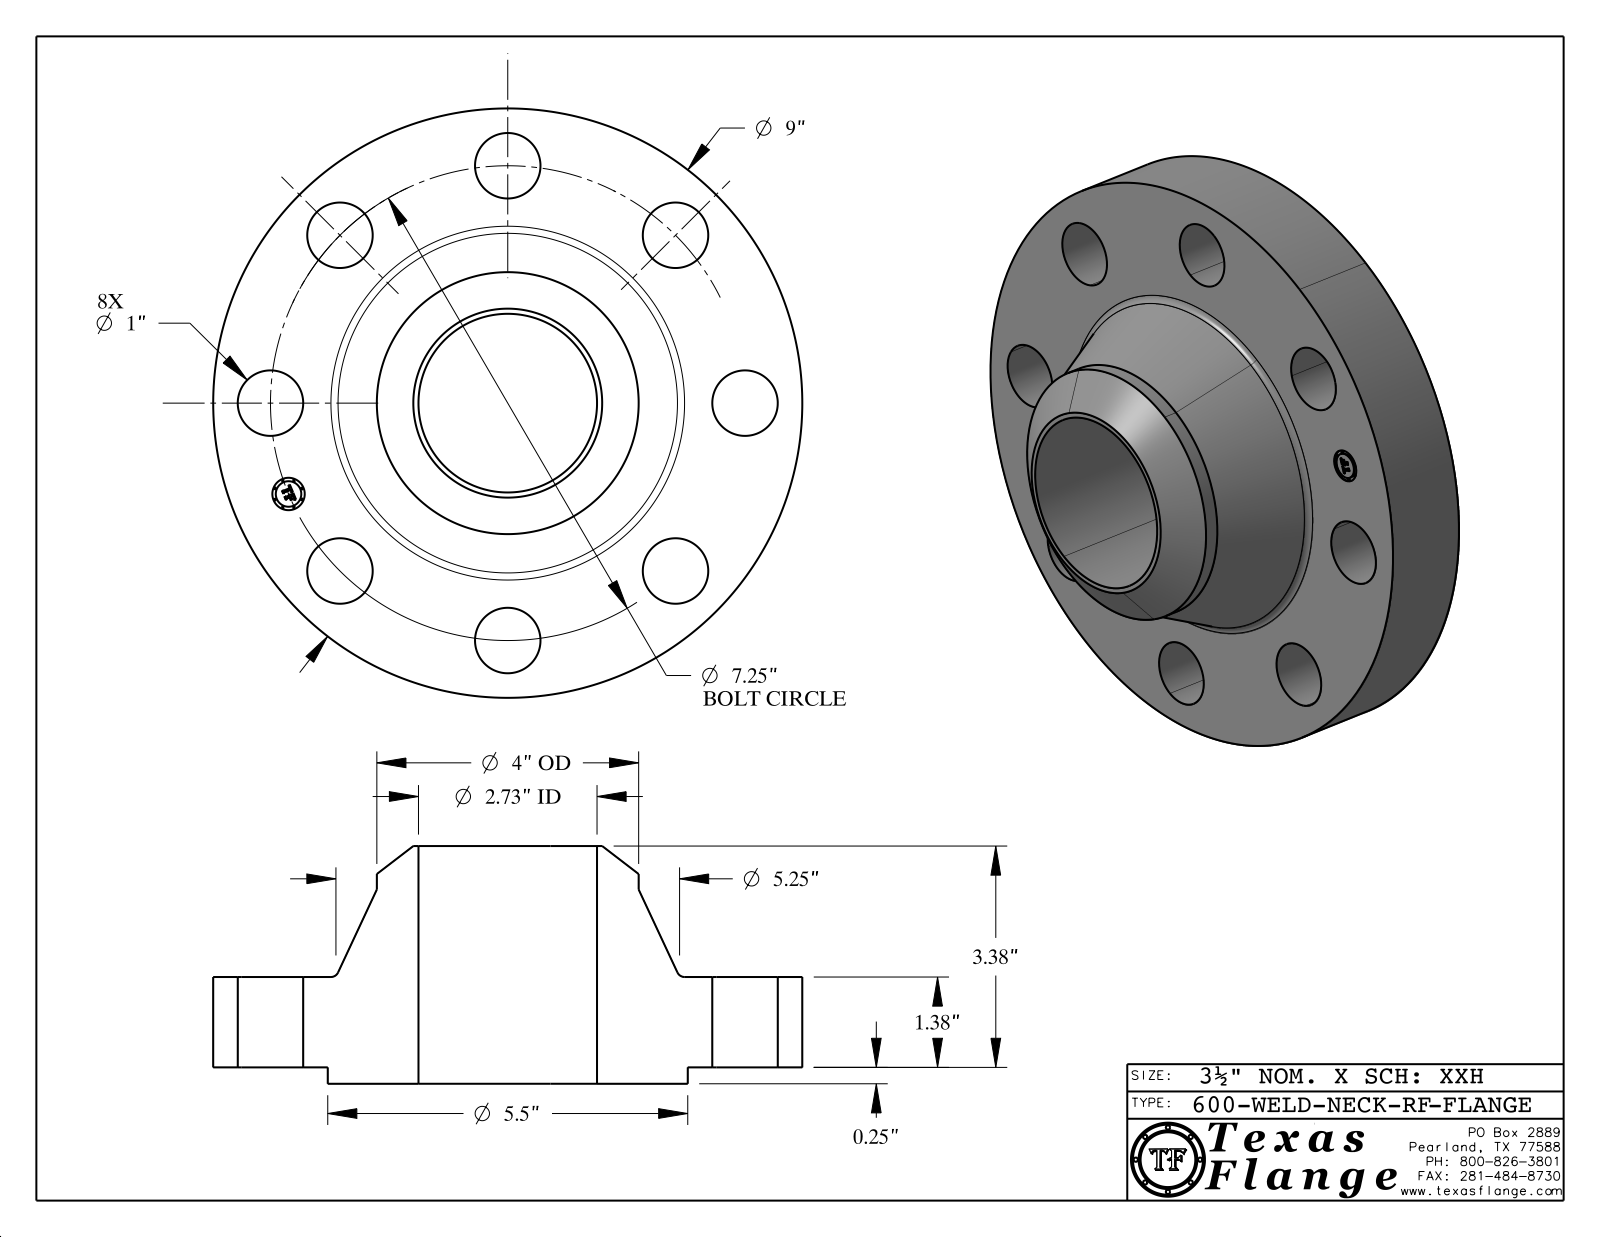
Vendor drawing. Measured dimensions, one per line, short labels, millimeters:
name: 600-WELD-NECK-RF
written by: CATIA V5 STEP AP214 (AUTOMOTIVE_DESIGN)
unit: mm
bodies: 1 solid, 419 faces (369 planar, 44 cylindrical, 6 other)
size: 228.6 × 228.6 × 92.2
volume: 1 531 000 mm³; area: 147 600 mm²
holes: 8× ⌀25.4, 1× ⌀12.6, 1× ⌀69.3
bosses: 8× ⌀0.8, 1× ⌀228.6, 1× ⌀139.7, 1× ⌀101.6, 1× ⌀9.9
face distances: 35.1, 6.4, 41.4, 92.2, 85.9, 50.8, 41, 34.7, 0.4, 51.2
hole spacings: 92.1, 70.5, 130.2, 170.1, 184.2, 35.9, 180.6, 102.3
